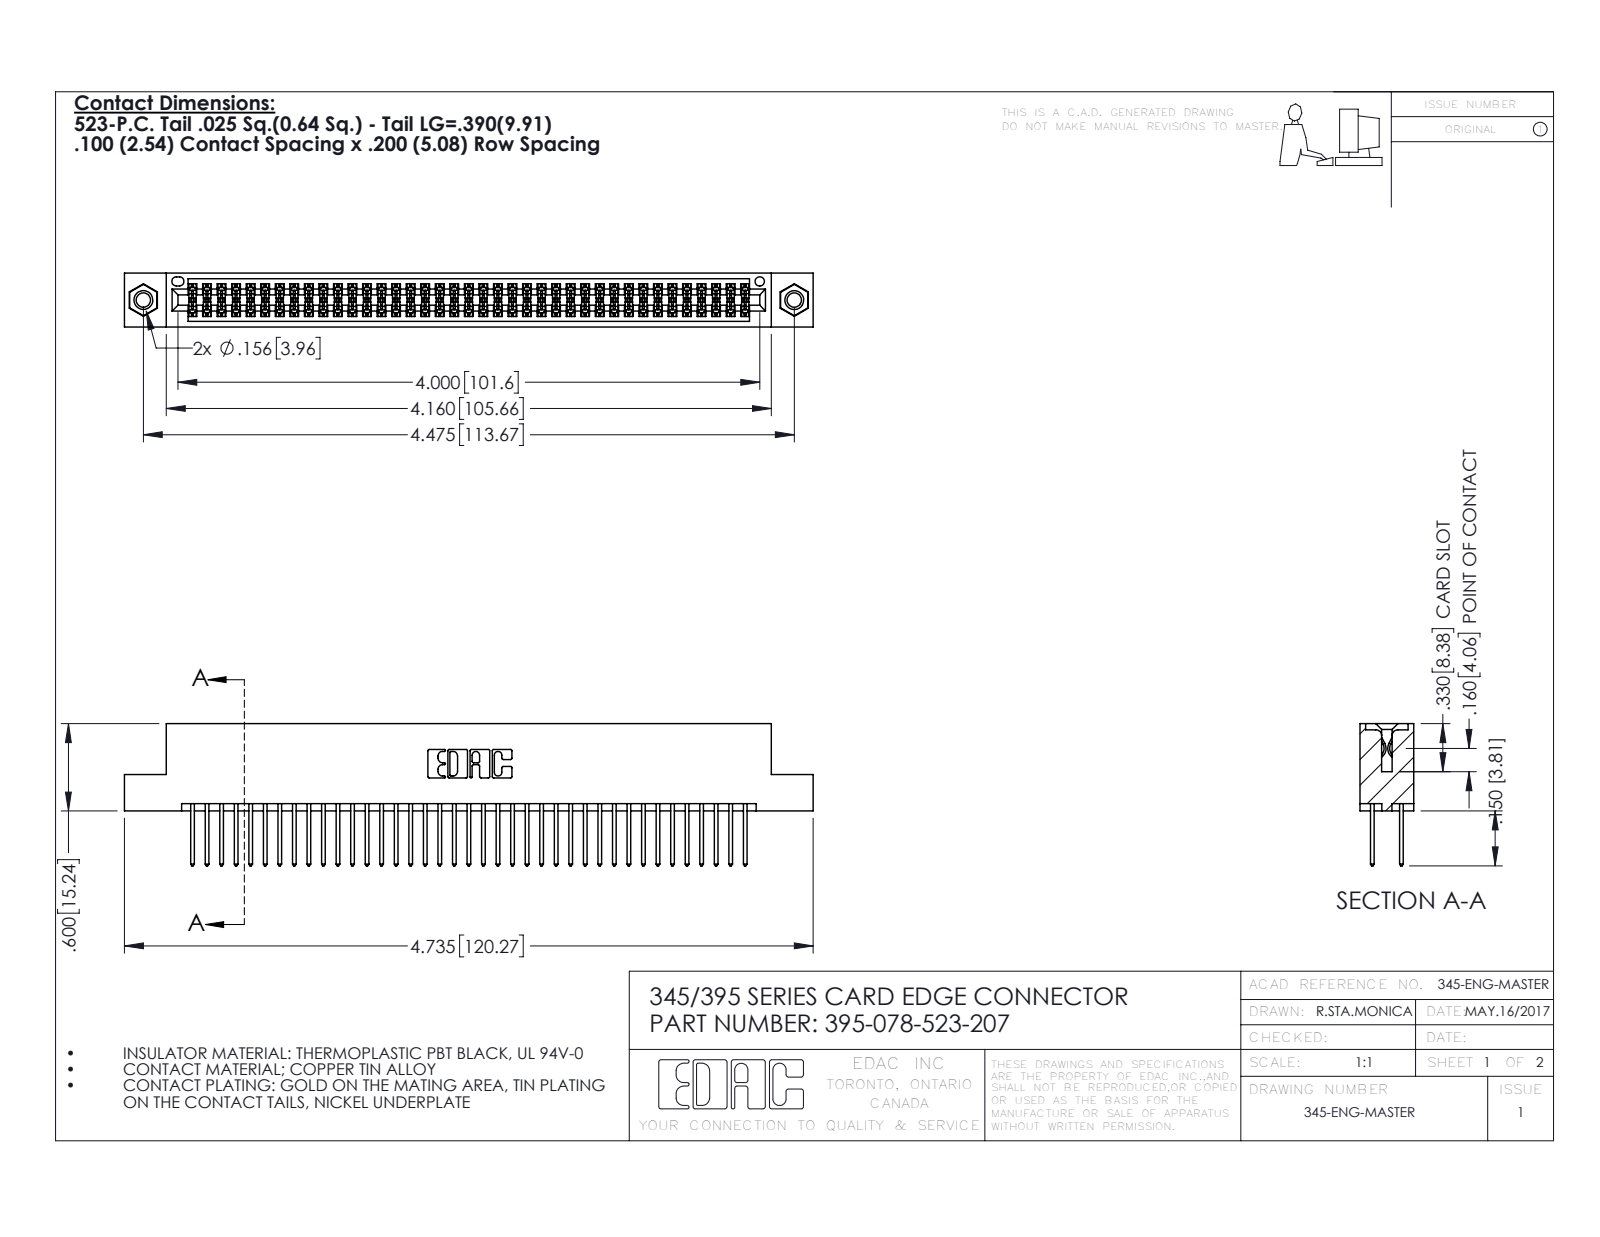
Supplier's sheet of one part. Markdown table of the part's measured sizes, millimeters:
| quantity | value |
| --- | --- |
| part name | 345-292-001_345-293-123; 345-250-001_345-250-005-103; 345 Part_Flush Mounting Lugs - 0.156 Dia-TI; 395-078-523-207 |
| STEP written by | SolidWorks 2016 (CONFIG_CONTROL_DESIGN) |
| units | millimeters |
| bodies | 81 solids, 4086 faces (2686 planar, 1384 cylindrical, 16 other) |
| overall size | 120.3 × 24.8 × 9.4 |
| volume | 11 800 mm³ |
| surface area | 18 130 mm² |
| round holes (diameter × count) | 2.5 × 2, 3.2 × 2, 4 × 2, 1.6 × 1 |
| round bosses / shafts (diameter × count) | 3.9 × 2 |
| partial cylindrical surfaces (radius × count) | 0.2 × 117, 0.3 × 78, 0.3 × 22, 0.2 × 6, 0.8 × 6, 0.7 × 3, 0.4 × 2, 0.5 × 2 |
| main face-to-face distances | 1.8, 7.6, 5.1, 2.5, 6.9, 0.6, 9.4, 5.7, 4.4, 3.8 |
| hole center spacings | 6.9, 107.7, 113.7 |
